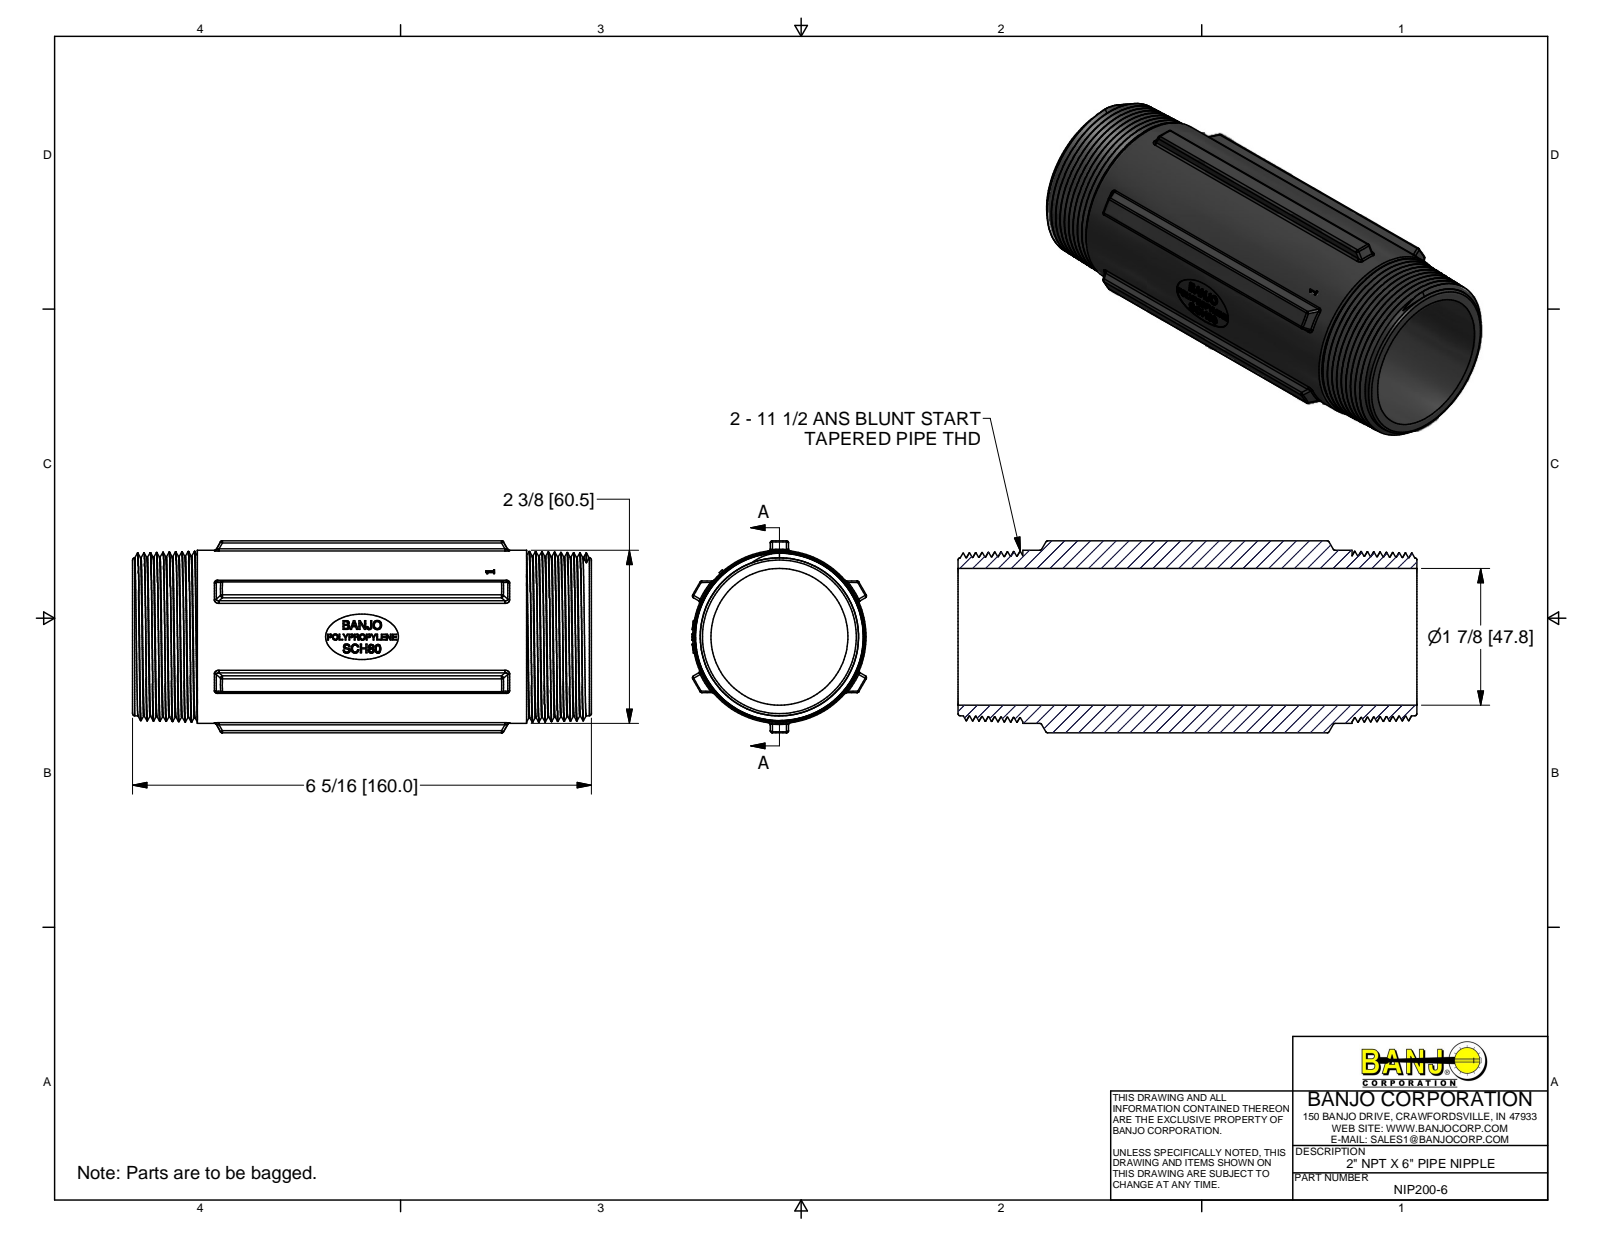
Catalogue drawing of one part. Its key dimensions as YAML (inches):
part_name: "NIP200-6"
step_written_by: "Autodesk Inventor 2013 (AUTOMOTIVE_DESIGN)"
units: inches
bodies: {solids: 1, faces: 527, planar: 186, cylindrical: 64, other: 277}
overall_size: [6.3, 2.64, 2.395]
volume: 10.59
surface_area: 101
round_holes:
  - {diameter: 1.88, count: 1}
round_bosses_or_shafts:
  - {diameter: 2.38, count: 1}
partial_cylinders:
  - {radius: 0.03, count: 24}
  - {radius: 1.18, count: 1}
  - {radius: 1.2, count: 1}
  - {radius: 1.21, count: 1}
face_to_face_distances: [2.64, 0.552, 2.088, 0.25, 1.536, 6.3, 0.89, 5.41, 4.52, 0.015]
